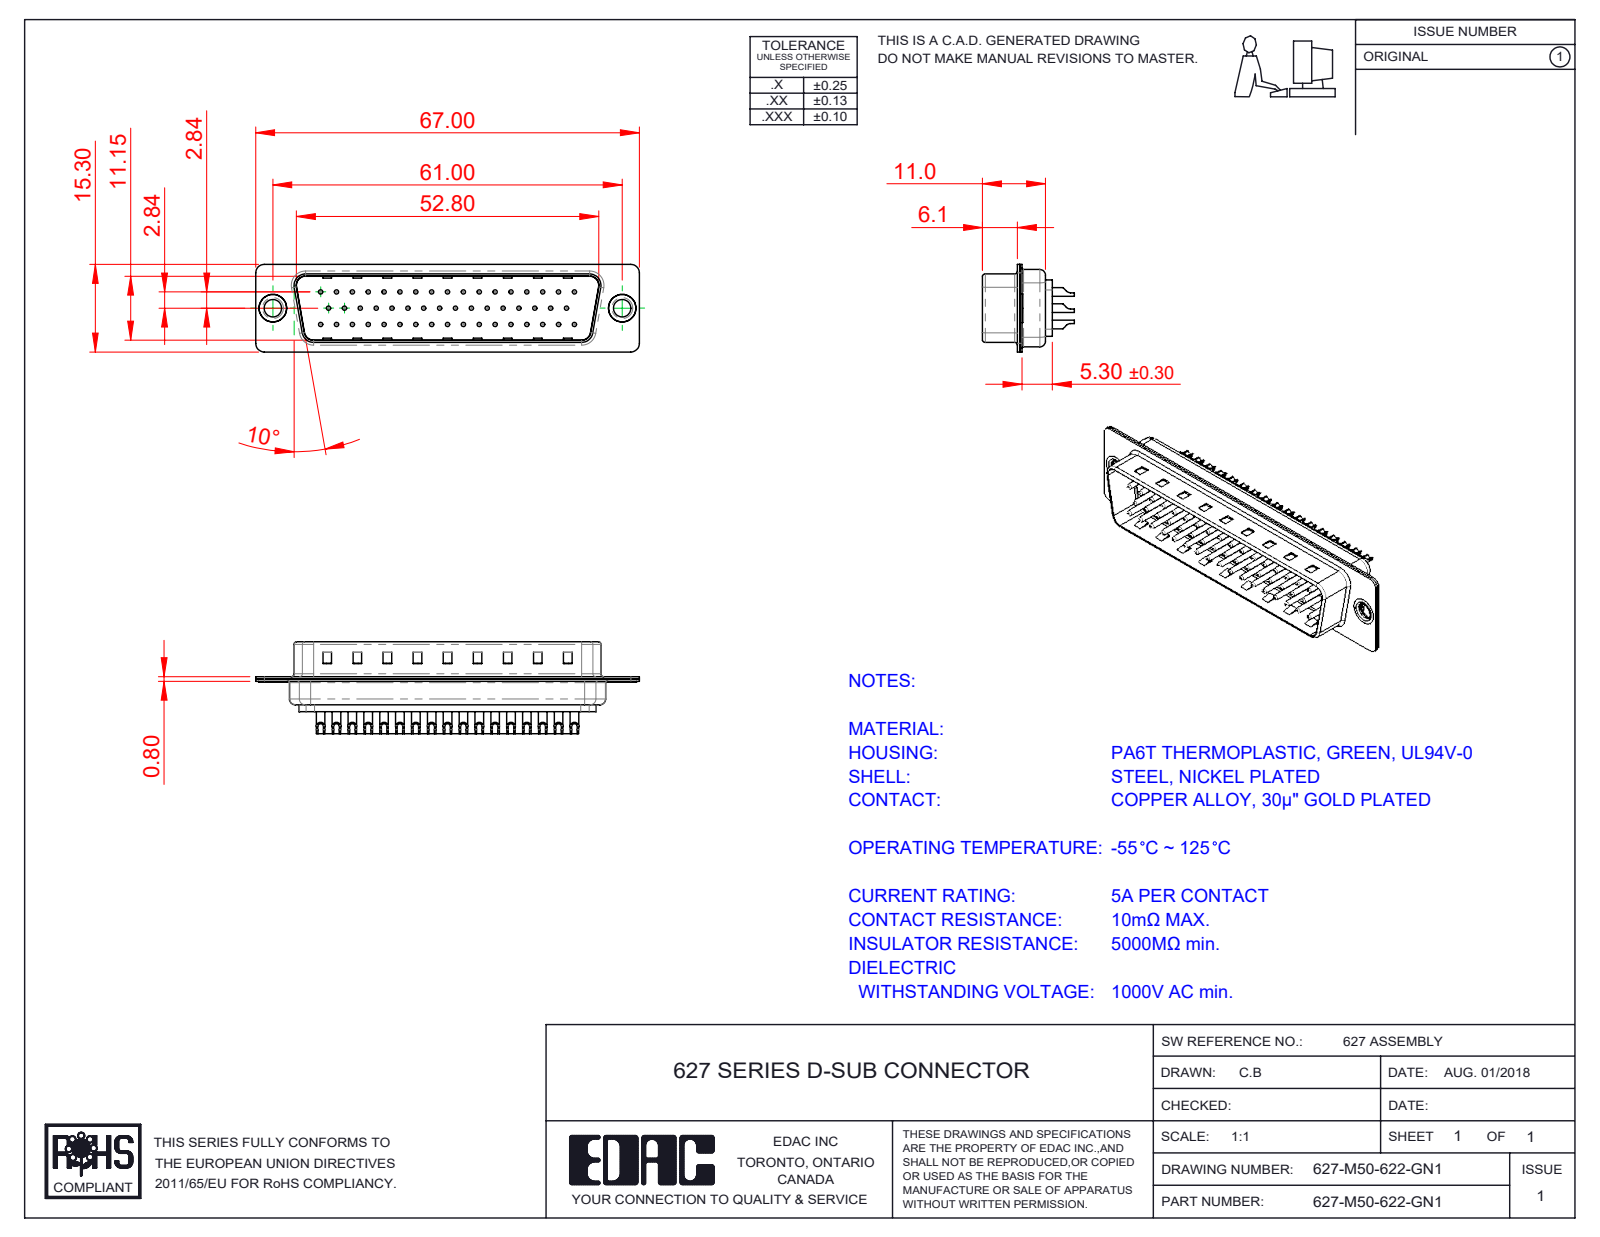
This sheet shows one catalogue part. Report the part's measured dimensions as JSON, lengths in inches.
{"part_name": "627M Contact Row 2_22L; 627M Housing_50 Contacts; 627M Contact Row 1_22; 627M Shell Front_50 Contacts (+4 more)", "step_written_by": "SolidWorks 2020 (CONFIG_CONTROL_DESIGN)", "units": "inches", "bodies": {"solids": 55, "faces": 2236, "planar": 653, "cylindrical": 925, "other": 658}, "overall_size": [2.638, 0.632, 0.602], "volume_in3": 0.278, "surface_area_in2": 17.08, "round_holes": [[0.03, 50], [0.039, 50], [0.063, 50], [0.079, 50], [0.12, 2], [0.157, 2], [0.189, 2]], "round_bosses_or_shafts": [[0.059, 50], [0.197, 2], [0.193, 2], [0.14, 2]], "partial_cylinders_radius": [[0.059, 16], [0.079, 12], [0.02, 8], [0.063, 8], [0.039, 7], [0.01, 4], [0.024, 4], [0.026, 4]], "face_to_face_distances": [0.016, 0.455, 0.224, 0.24, 0.031, 0.03, 0.485, 0.485, 0.516, 0.209], "hole_center_spacings": [0.124, 0.109, 0.218, 0.327, 0.436, 0.545, 0.654, 0.198]}
